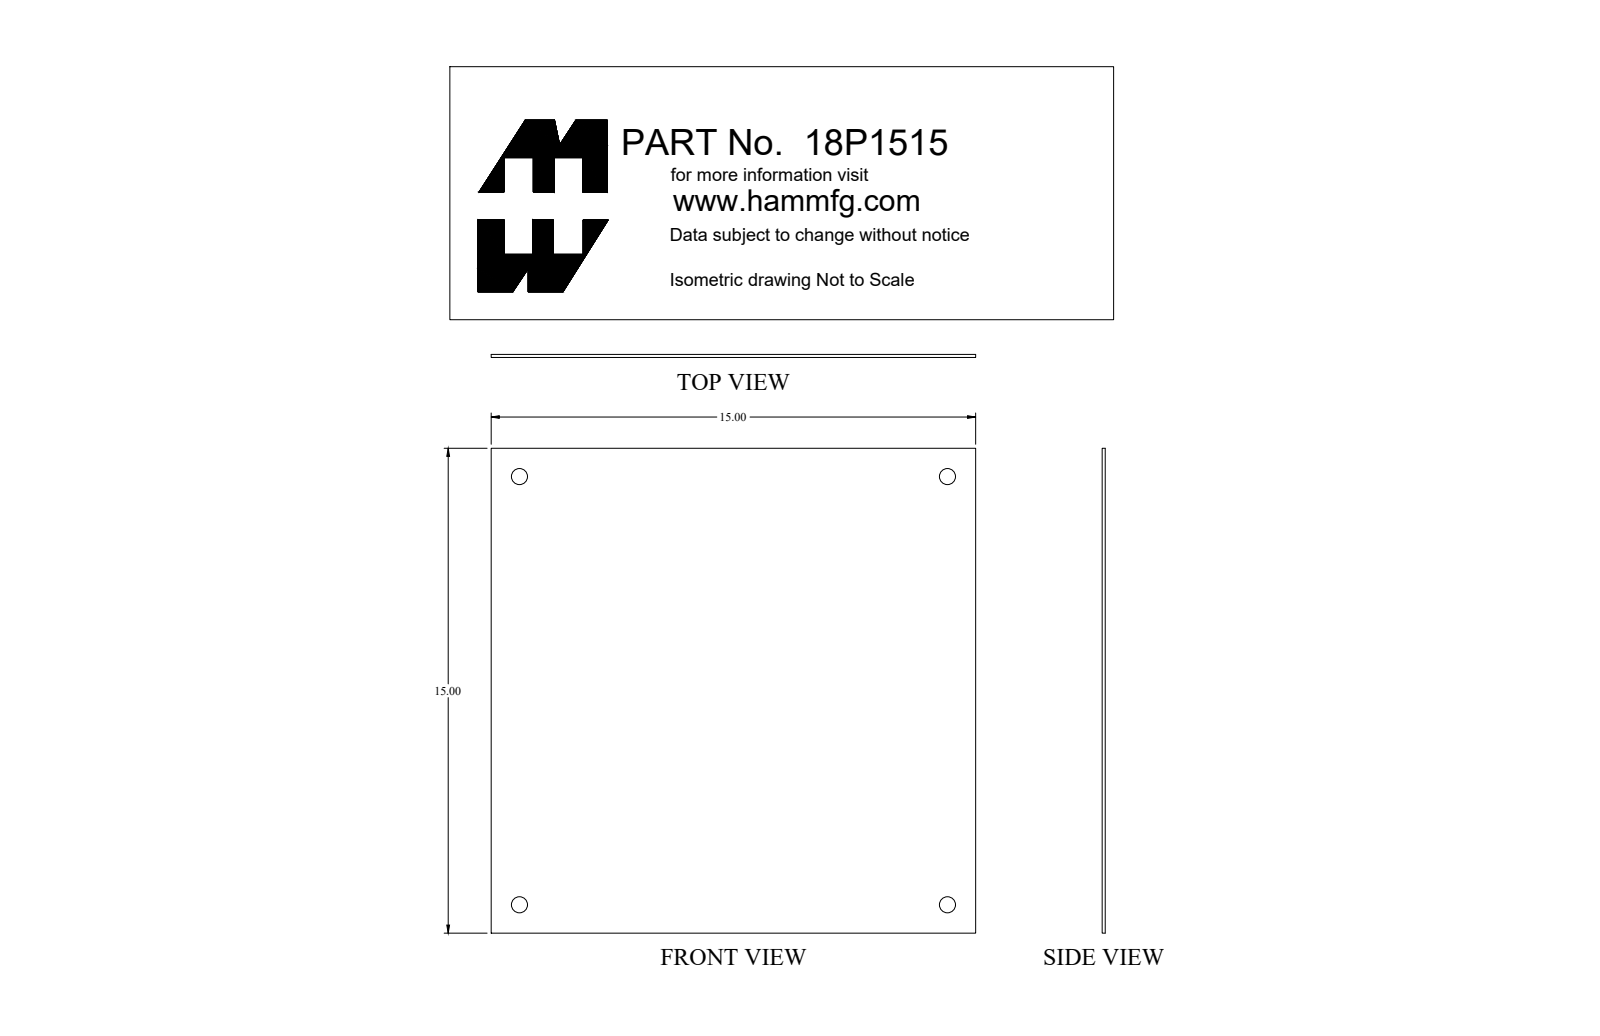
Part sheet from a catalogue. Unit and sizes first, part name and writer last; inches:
Units: inches
Overall size (bounding box): 15 × 15 × 0.095
Round holes (diameter × count): ⌀0.5 ×4
Main face-to-face distances: 0.095, 15
Hole centre spacings: 13.25, 18.739
Volume: 21.3 in³ · Surface area: 454.7 in²
Bodies: 1 solid, 14 faces (6 planar, 8 cylindrical, 0 other)
Part name (STEP PRODUCT): 18P1515_Default
STEP written by: SolidWorks 2018 (CONFIG_CONTROL_DESIGN)
